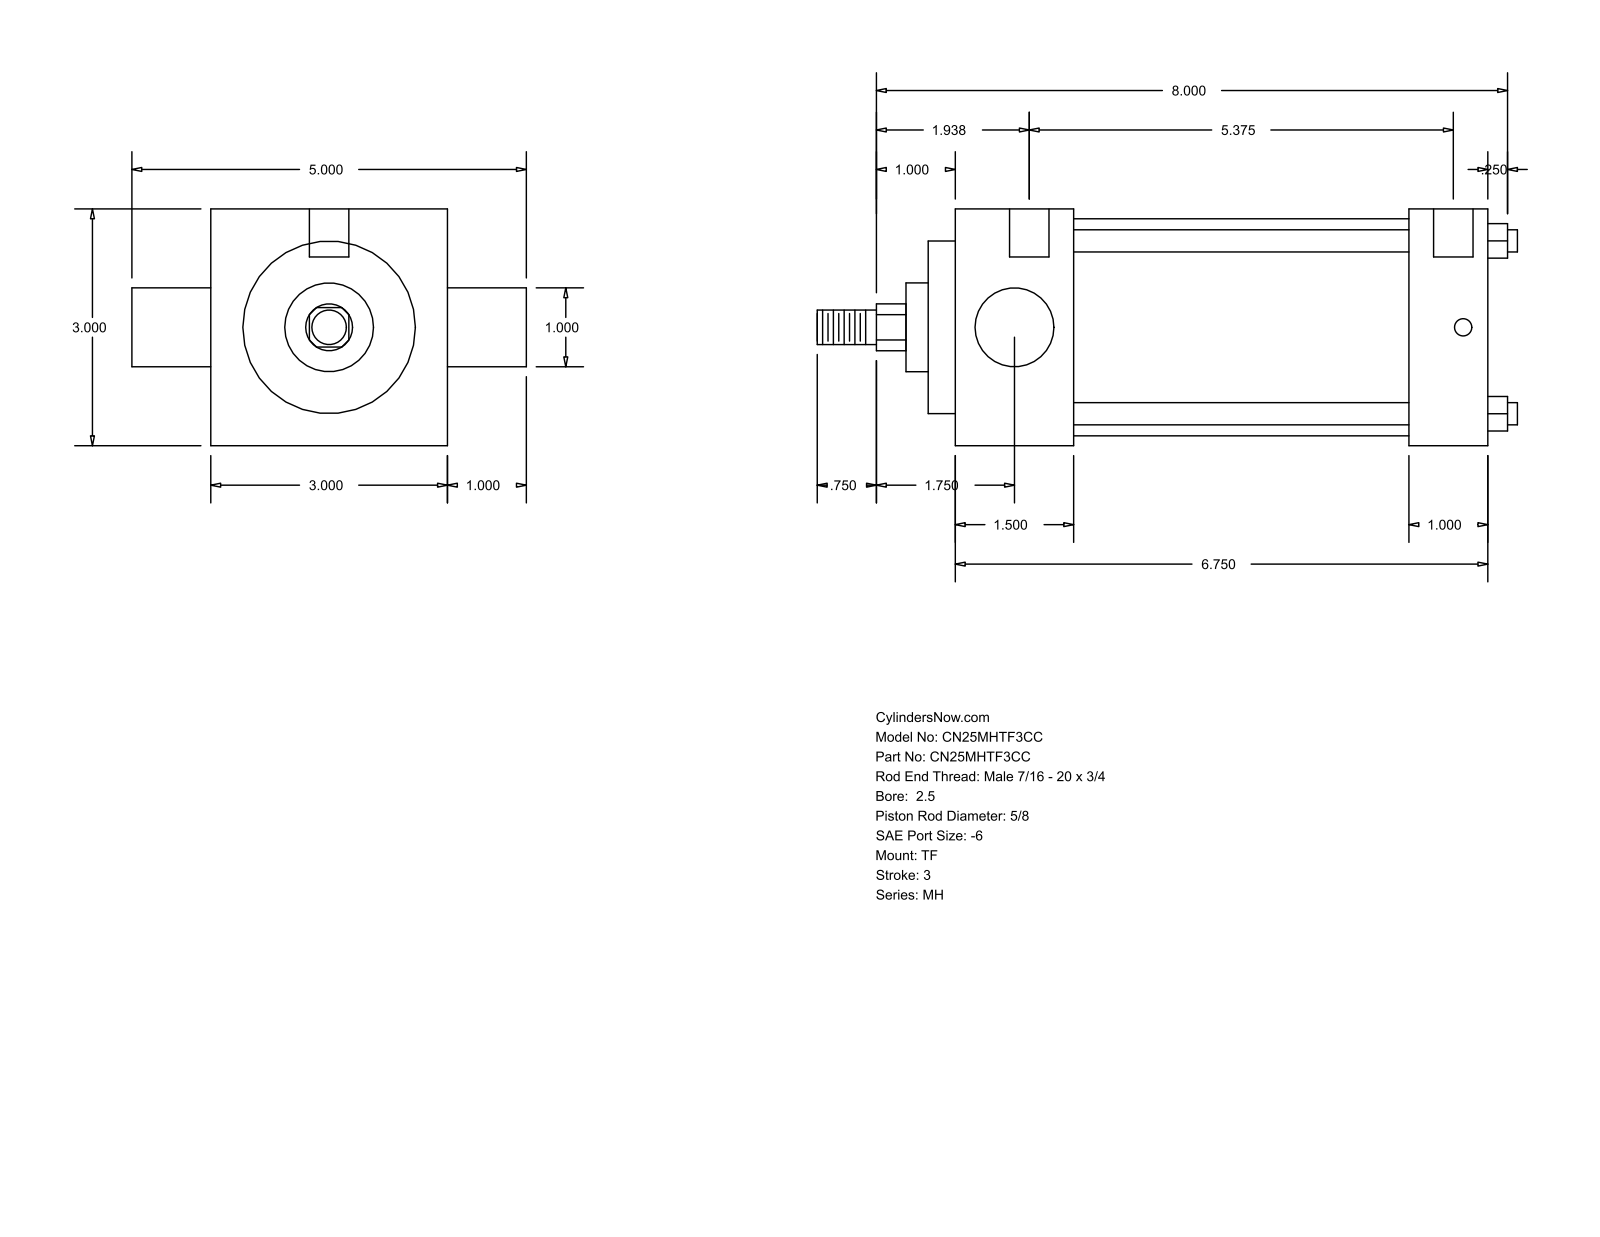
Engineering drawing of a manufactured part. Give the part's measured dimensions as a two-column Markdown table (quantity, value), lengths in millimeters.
| quantity | value |
| --- | --- |
| part name | MH_TF__0250_0.625 |
| STEP written by | GSSL Pune (CONFIG_CONTROL_DESIGN) |
| units | millimeters |
| bodies | 0 solids, 86 faces (61 planar, 25 cylindrical, 0 other) |
| overall size | 225.43 × 127 × 76.2 |
| round holes (diameter × count) | 5.56 × 3, 12.7 × 2 |
| round bosses / shafts (diameter × count) | 7.14 × 4, 69.85 × 1, 55.55 × 1, 28.57 × 1, 25.4 × 1, 15.88 × 1, 11.11 × 1 |
| partial cylindrical surfaces (radius × count) | 7.54 × 1 |
| main face-to-face distances | 76.2, 171.45, 25.4, 38.1, 133.35, 146.05, 107.95, 8.73, 46.83, 154.78 |
| hole center spacings | 3.17, 4.76, 136.53, 139.7, 141.29, 144.46 |
